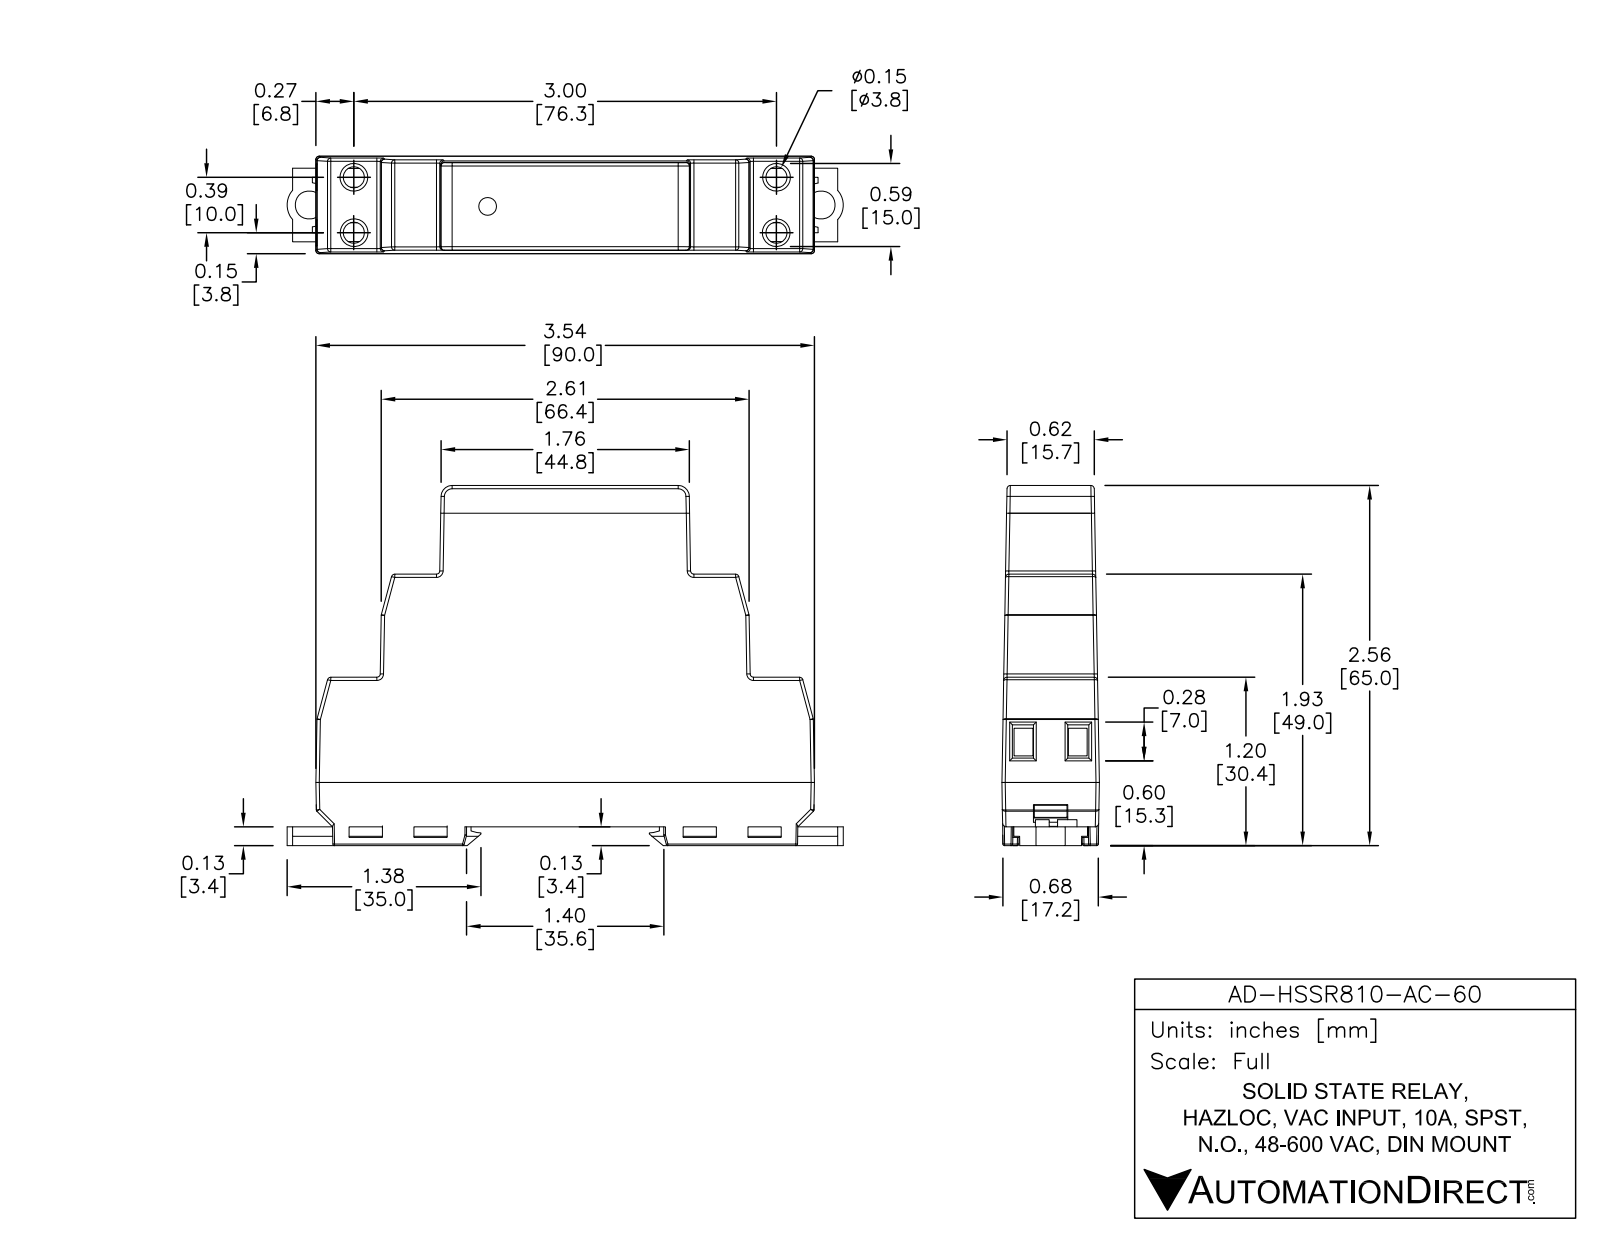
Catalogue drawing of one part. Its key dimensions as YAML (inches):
part_name: "AD-HSSR810-AC-60"
step_written_by: "SolidWorks 2013 (AUTOMOTIVE_DESIGN)"
units: inches
bodies: {solids: 35, faces: 1262, planar: 683, cylindrical: 65, other: 514}
overall_size: [3.952, 2.619, 0.692]
volume: 4.725
surface_area: 25.56
round_holes:
  - {diameter: 0.2, count: 4}
  - {diameter: 0.19, count: 2}
round_bosses_or_shafts:
  - {diameter: 0.175, count: 4}
  - {diameter: 0.1, count: 1}
partial_cylinders:
  - {radius: 0.02, count: 10}
  - {radius: 0.024, count: 10}
  - {radius: 0.012, count: 6}
  - {radius: 0.079, count: 2}
  - {radius: 0.15, count: 2}
  - {radius: 45.93, count: 2}
face_to_face_distances: [0.136, 2.559, 2.423, 0.134, 2.425, 1.929, 1.795, 1.793, 0.63, 1.197]
hole_center_spacings: [3.335, 0.379, 0.38, 0.4, 3.006, 3.033, 3.652]
